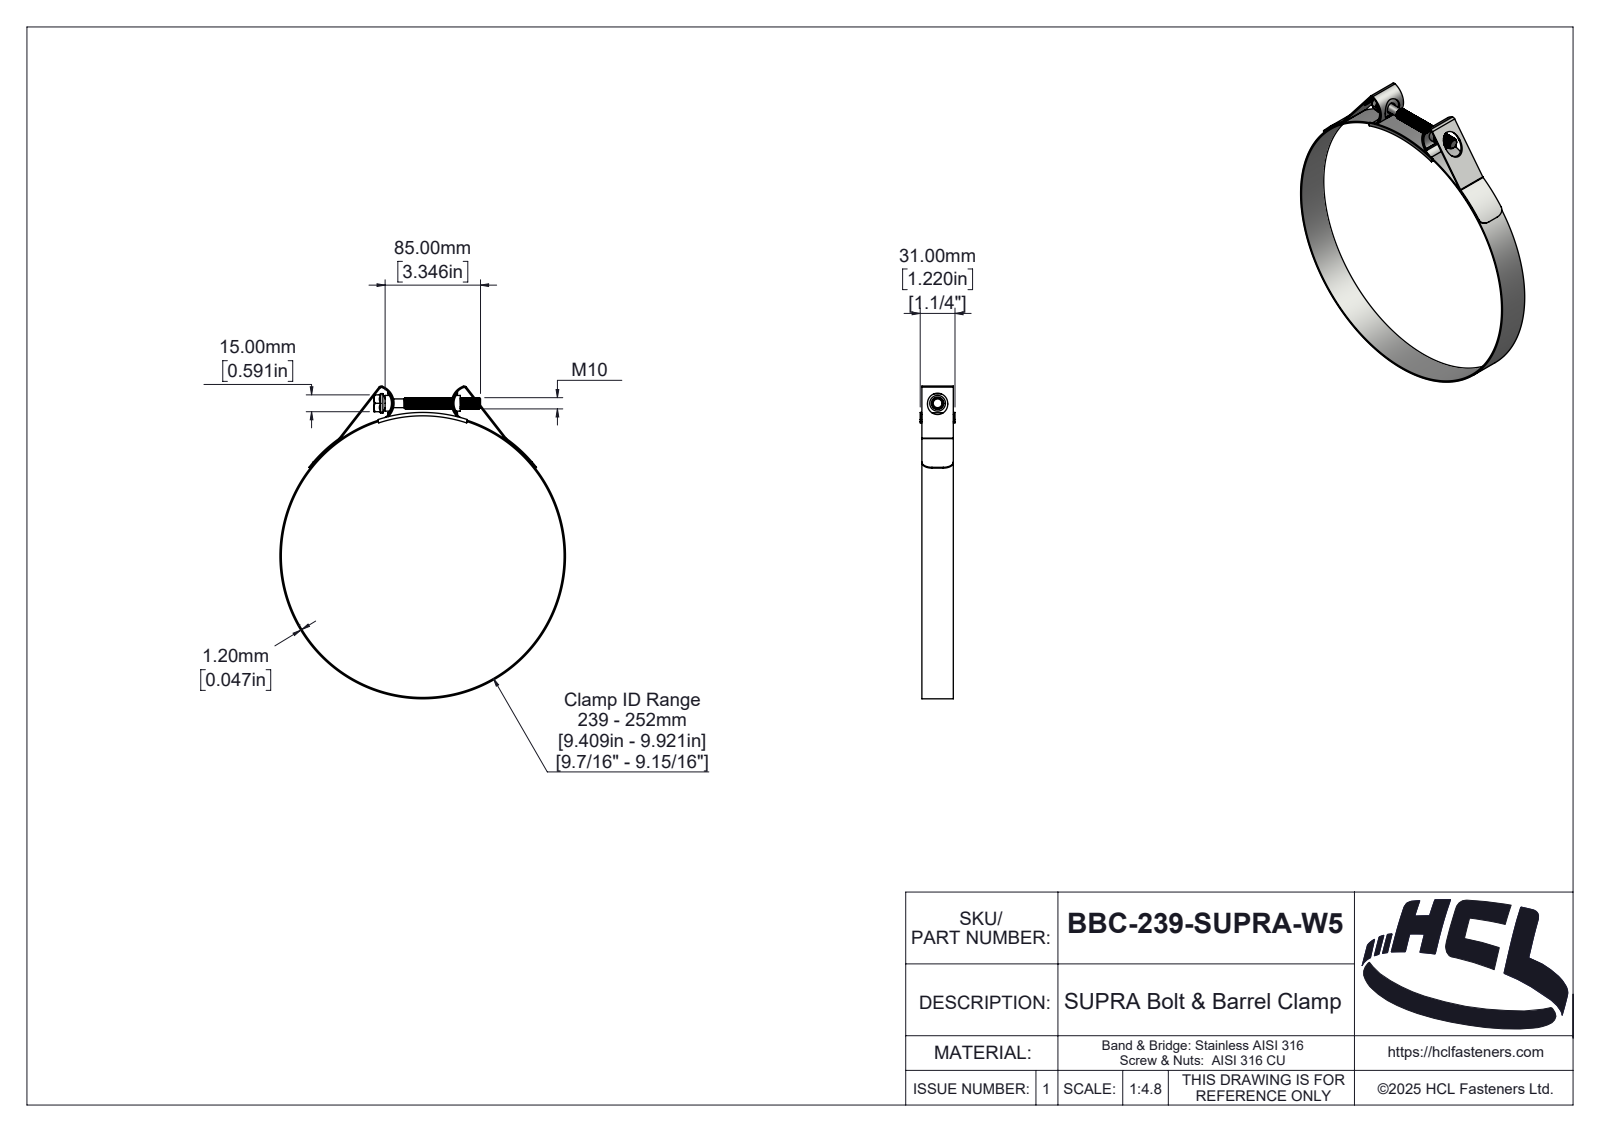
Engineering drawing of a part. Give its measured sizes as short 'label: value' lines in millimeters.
name: BBC-239-SUPRA-W5
written by: SolidWorks 2025 (AUTOMOTIVE_DESIGN)
unit: mm
bodies: 5 solids, 381 faces (50 planar, 245 cylindrical, 86 other)
size: 278.51 × 254.4 × 31
volume: 44 427 mm³; area: 69 220 mm²
holes: 1× ⌀252
bosses: 1× ⌀254.4, 1× ⌀17.32, 1× ⌀14, 1× ⌀10, 1× ⌀7.8
rounds: 4× R1, 2× R1.3, 2× R2, 2× R2.5, 2× R3.2, 2× R9, 2× R13.91, 2× R14.91
face distances: 1.2, 28, 1.5, 29.5, 29.8, 28.3, 31, 28.6, 2.5, 64.5
